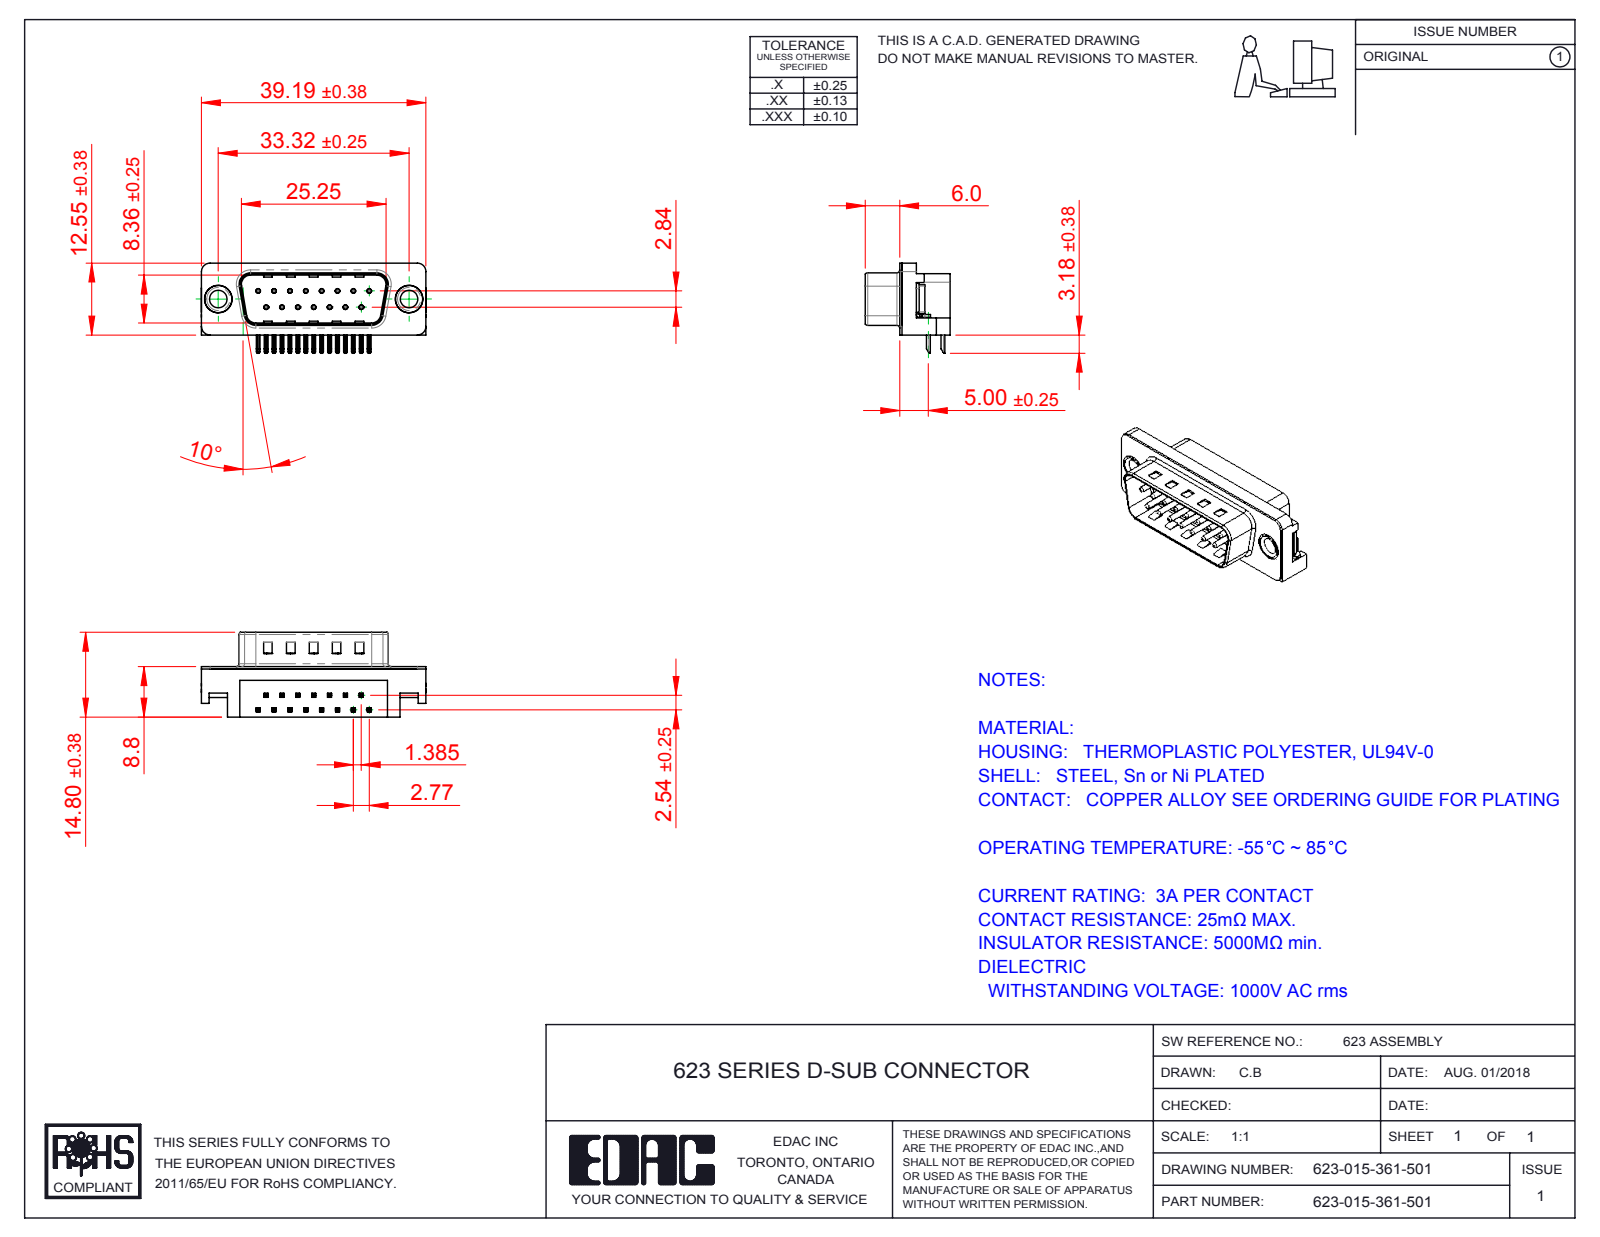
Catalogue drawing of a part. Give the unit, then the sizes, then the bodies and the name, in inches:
Units: inches
Overall size (bounding box): 1.544 × 0.619 × 0.583
Round holes (diameter × count): ⌀0.014 ×15, ⌀0.031 ×15, ⌀0.12 ×2, ⌀0.157 ×2, ⌀0.189 ×2, ⌀0.197 ×2
Round bosses / shafts (diameter × count): ⌀0.03 ×15, ⌀0.193 ×2, ⌀0.187 ×2, ⌀0.152 ×2
Partial cylindrical surfaces — rounded edges, fillets, slot ends (radius × count): R0.01 ×68, R0.005 ×30, R0.039 ×16, R0.02 ×9, R0.059 ×6, R0.035 ×4, R0.063 ×4, R0.079 ×4
Main face-to-face distances: 0.016, 0.331, 0.083, 0.067, 0.346, 0.412, 0.428, 0.345, 0.232, 0.114
Hole centre spacings: 0.124, 0.109, 0.218, 0.327, 0.436, 0.198, 0.198, 0.294
Volume: 0.202 in³ · Surface area: 7.535 in²
Bodies: 21 solids, 1427 faces (893 planar, 417 cylindrical, 117 other)
Part name (STEP PRODUCT): 623 Thru Hole Rivet; 623 Contact Bottom; 623 Non Board Mount; 623-015-361-501 (+3 more)
STEP written by: SolidWorks 2016 (CONFIG_CONTROL_DESIGN)
